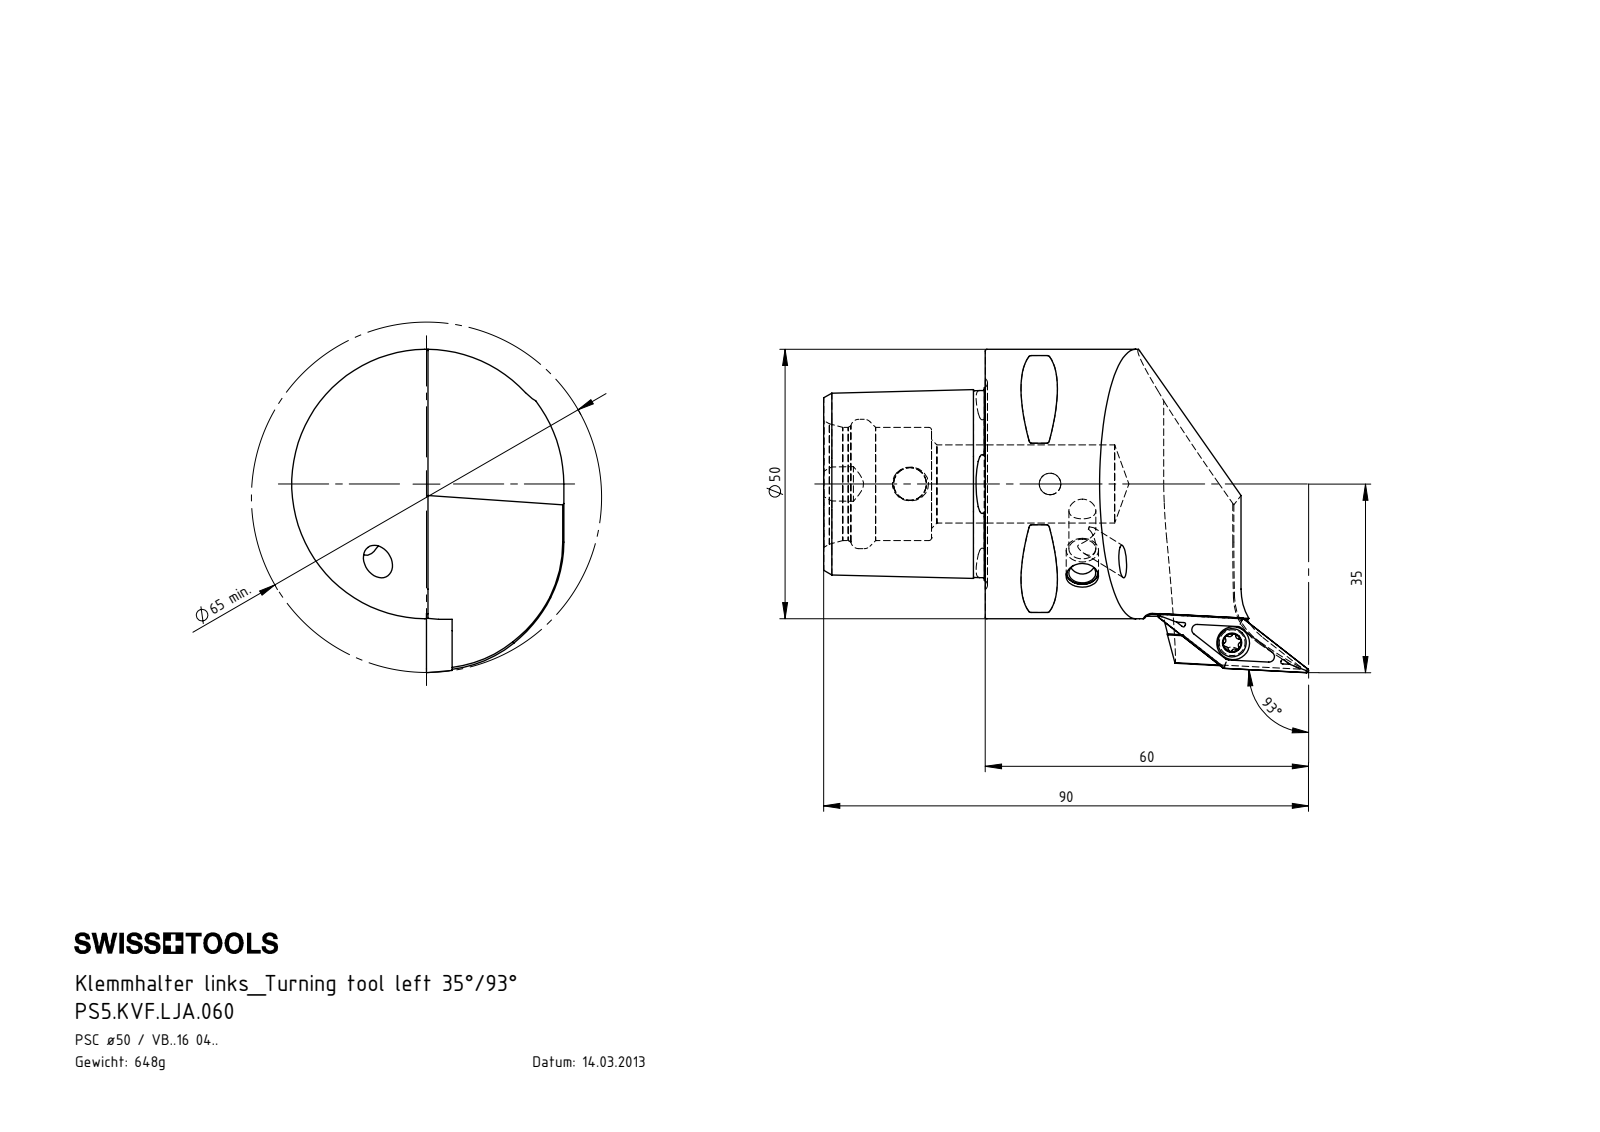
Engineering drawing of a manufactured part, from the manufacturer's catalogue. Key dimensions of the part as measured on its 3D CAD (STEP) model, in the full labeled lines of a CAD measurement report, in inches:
Part name (STEP PRODUCT): VBMT160404; WCB-ER2.001.009_A; PS5.KVF.LJA.060; PS5-KVF.LJA.060_A (+1 more)
STEP written by: SolidWorks 2017 (AUTOMOTIVE_DESIGN)
Units: inches
Bodies: 5 solids, 203 faces (55 planar, 47 cylindrical, 101 other)
Overall size (bounding box): 3.543 × 2.382 × 1.988
Volume: 5.224 in³ · Surface area: 29.52 in²
Round holes (diameter × count): ⌀0.197 ×3, ⌀0.24 ×2, ⌀0.13 ×1, ⌀0.157 ×1, ⌀0.173 ×1, ⌀0.236 ×1, ⌀0.571 ×1, ⌀0.827 ×1, ⌀0.945 ×1
Round bosses / shafts (diameter × count): ⌀1.969 ×1, ⌀0.236 ×1, ⌀0.207 ×1, ⌀0.157 ×1
Partial cylindrical surfaces — rounded edges, fillets, slot ends (radius × count): R0.02 ×8, R0.013 ×6, R0.023 ×6, R0.006 ×2, R0.031 ×1, R0.134 ×1, R0.157 ×1, R0.433 ×1
Main face-to-face distances: 1.181, 0.176, 0.817, 0.992, 0.755, 1.748, 0.787, 0.394, 1.173, 0.386
Hole centre spacings: 1.024, 1.765, 1.773, 2.624, 2.633
